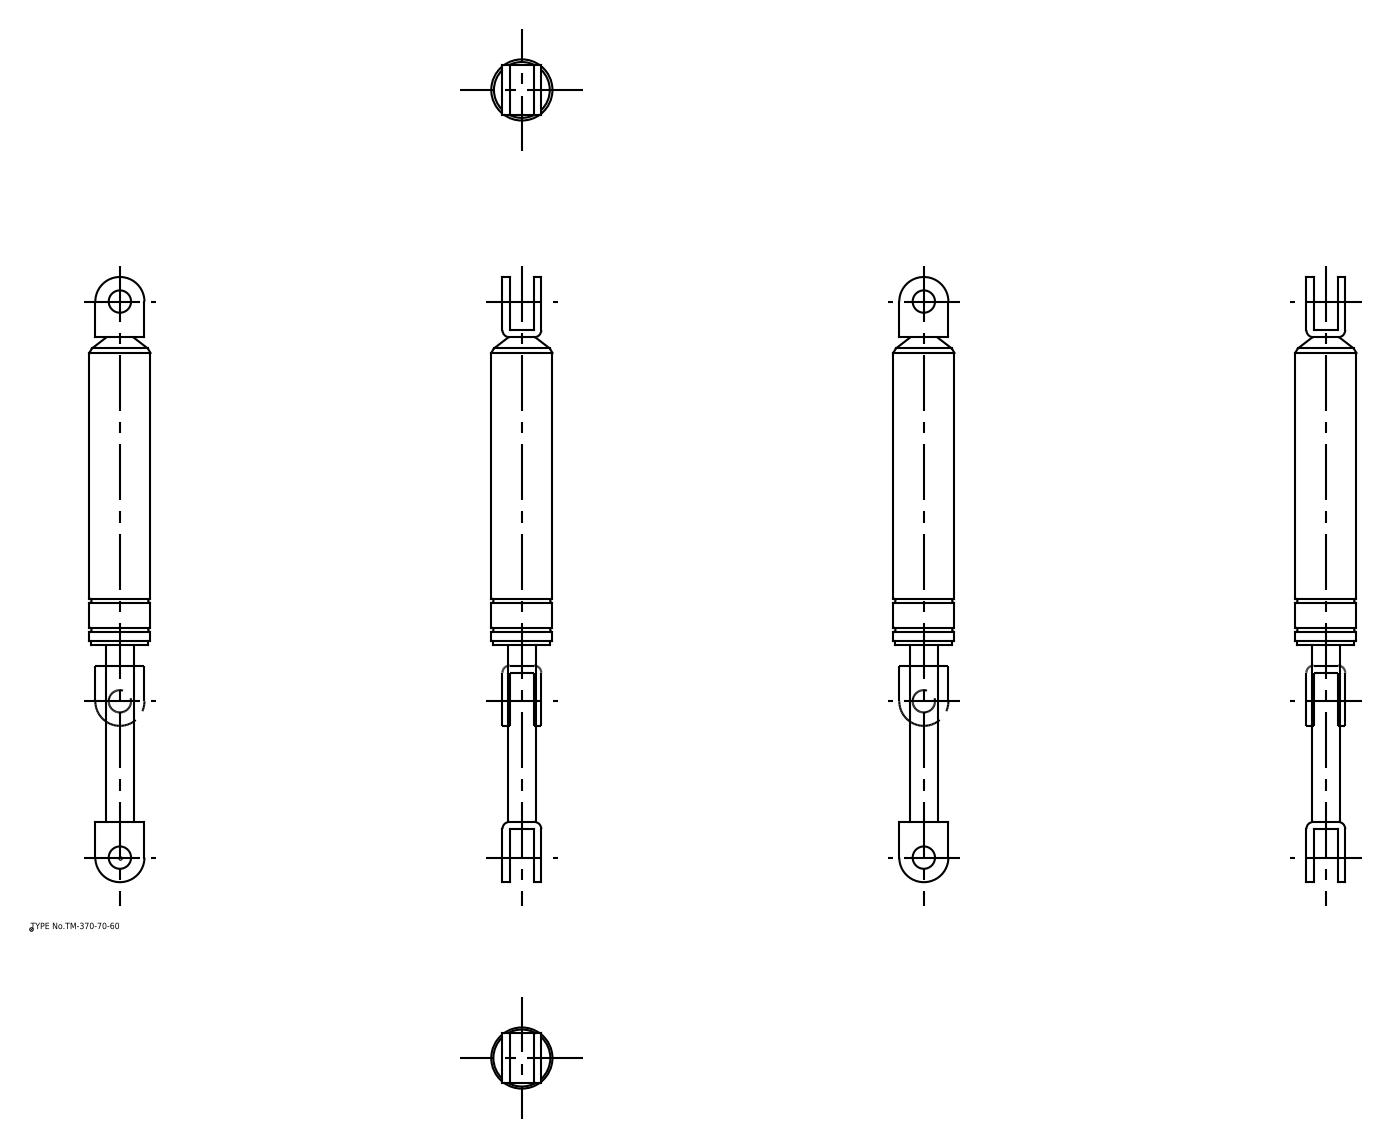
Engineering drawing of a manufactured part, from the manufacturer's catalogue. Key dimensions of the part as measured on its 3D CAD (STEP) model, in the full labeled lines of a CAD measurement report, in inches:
Part name (STEP PRODUCT): TM_370_70_60; TM_370_70_60_div
STEP written by: spGate 16.7.1 (AUTOMOTIVE_DESIGN)
Units: inches
Bodies: 2 solids, 64 faces (22 planar, 32 cylindrical, 10 other)
Overall size (bounding box): 10.669 × 1.11 × 1.11
Volume: 5.904 in³ · Surface area: 33.73 in²
Round holes (diameter × count): ⌀0.394 ×2
Round bosses / shafts (diameter × count): ⌀1.11 ×1, ⌀1.079 ×1, ⌀1.004 ×1, ⌀0.492 ×1
Partial cylindrical surfaces — rounded edges, fillets, slot ends (radius × count): R0.126 ×4, R0.433 ×2
Main face-to-face distances: 0.126, 0.559, 0.685, 0.433, 0.866, 8.669, 3.236, 8.795, 5.559, 5.433
Hole centre spacings: 9.803
